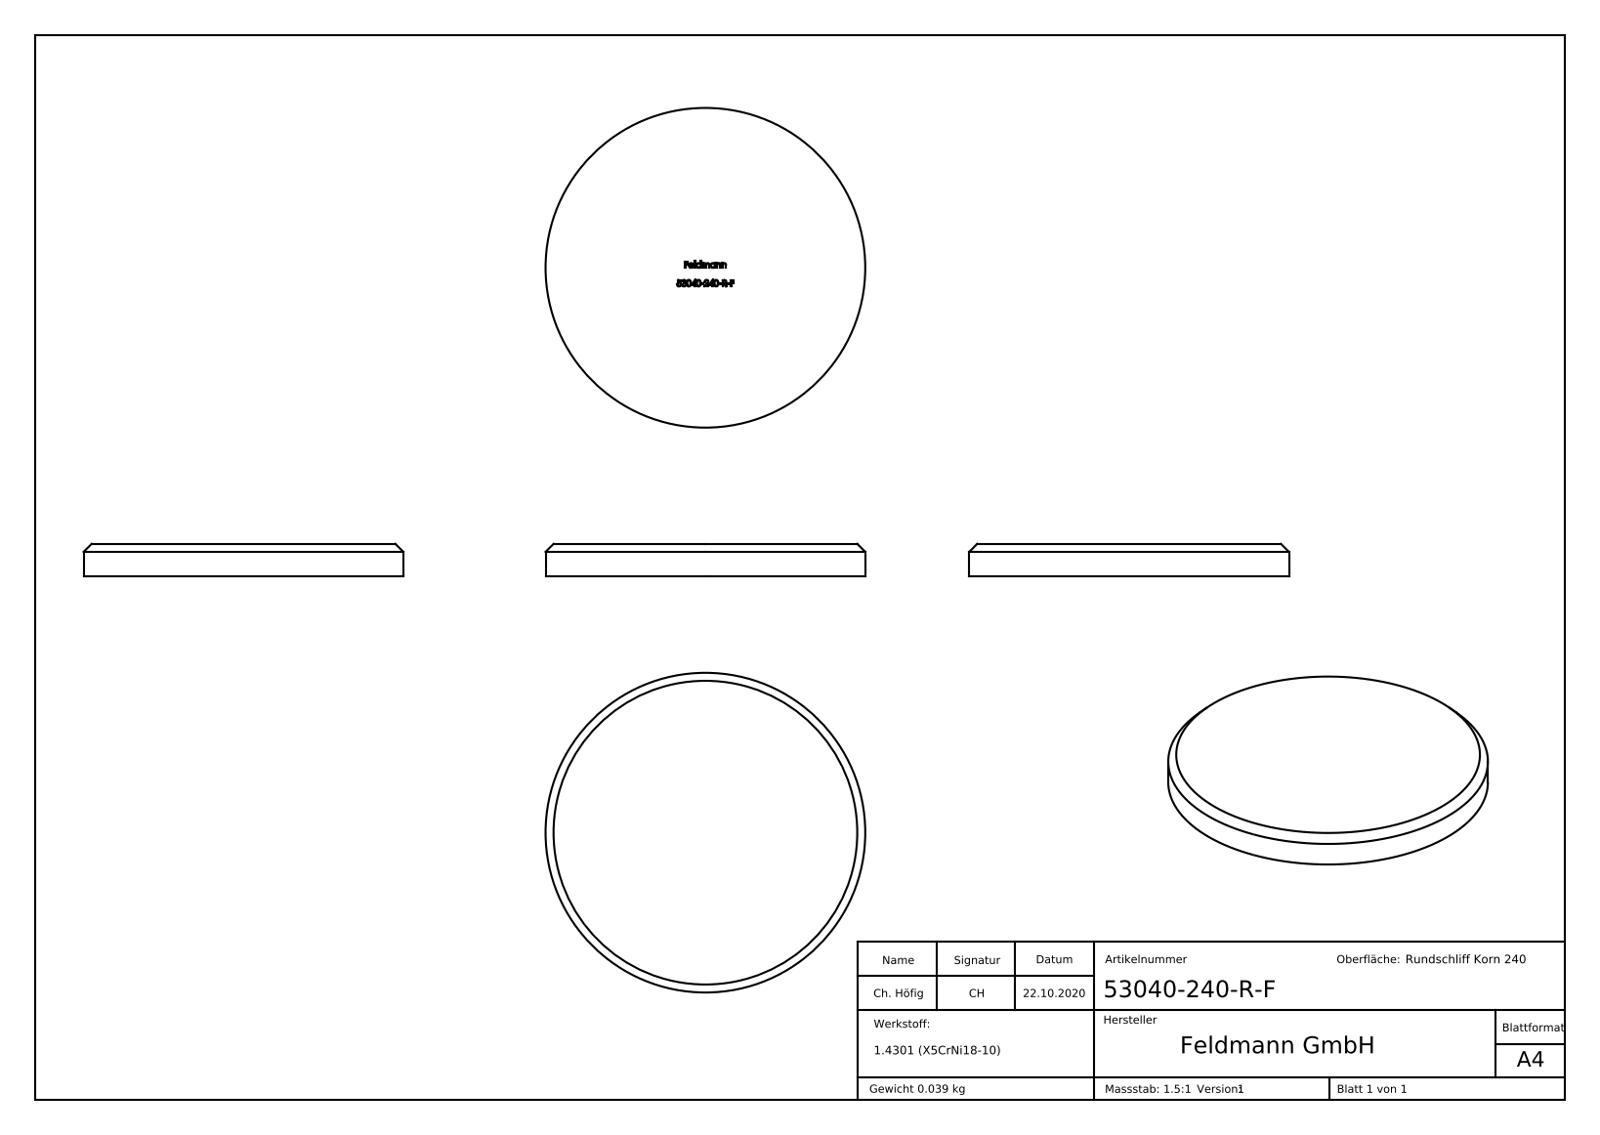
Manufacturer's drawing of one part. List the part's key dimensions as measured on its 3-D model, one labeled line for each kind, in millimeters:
Part name (STEP PRODUCT): 53040-240-R-F
STEP written by: SolidWorks 2018 (CONFIG_CONTROL_DESIGN)
Units: millimetres
Bodies: 1 solid, 272 faces (160 planar, 2 cylindrical, 110 other)
Overall size (bounding box): 40 × 40 × 4
Volume: 4 965 mm³ · Surface area: 2 948 mm²
Round bosses / shafts (diameter × count): ⌀40 ×1
Main face-to-face distances: 4, 3.9, 2.32, 1.21, 2.2, 3.49, 0.79, 1.29, 2.24, 1.78
